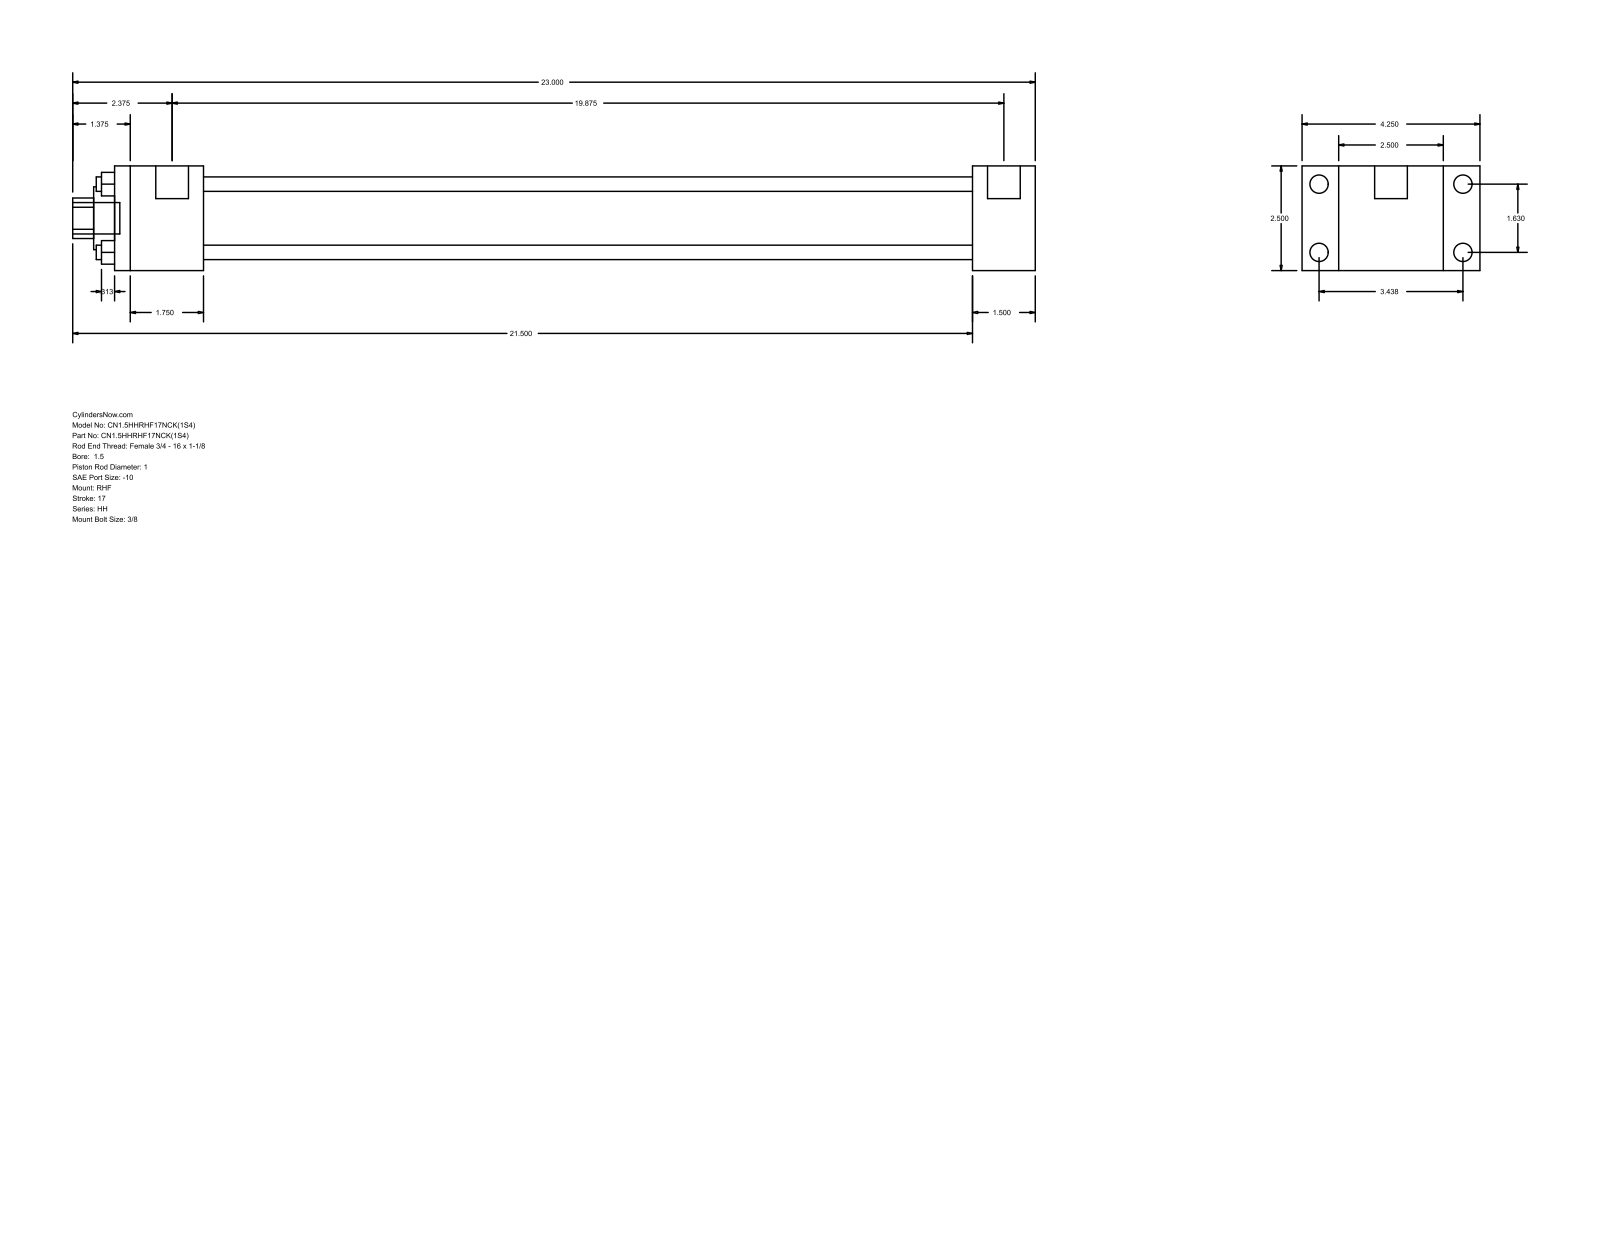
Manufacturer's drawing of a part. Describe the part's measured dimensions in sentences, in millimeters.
The part is named "HH_RHF__0150_1". Its 3-D file was written by "GSSL Pune (CONFIG_CONTROL_DESIGN)". It is 0 solids with 88 faces: 60 planar, 28 cylindrical and 0 other. Overall it measures 584.2 by 107.95 by 63.5 millimeters. Round holes: 4 of diameter 8.76, 1 of diameter 25.4, 1 of diameter 38.1, 1 of diameter 44.45. Round bosses or shafts: 4 of diameter 11.13, 4 of diameter 5.56, 2 of diameter 19.84, 1 of diameter 19.05. Partial cylindrical surfaces (rounded edges, fillets, slot ends): 1 of radius 12.29. The main face-to-face distances are 63.5, 22.23, 85.73, 38.1, 107.96, 466.72, 504.82, 53.98, 520.7, 558.8. The hole center spacings are 29.27, 41.4, 58.55.
